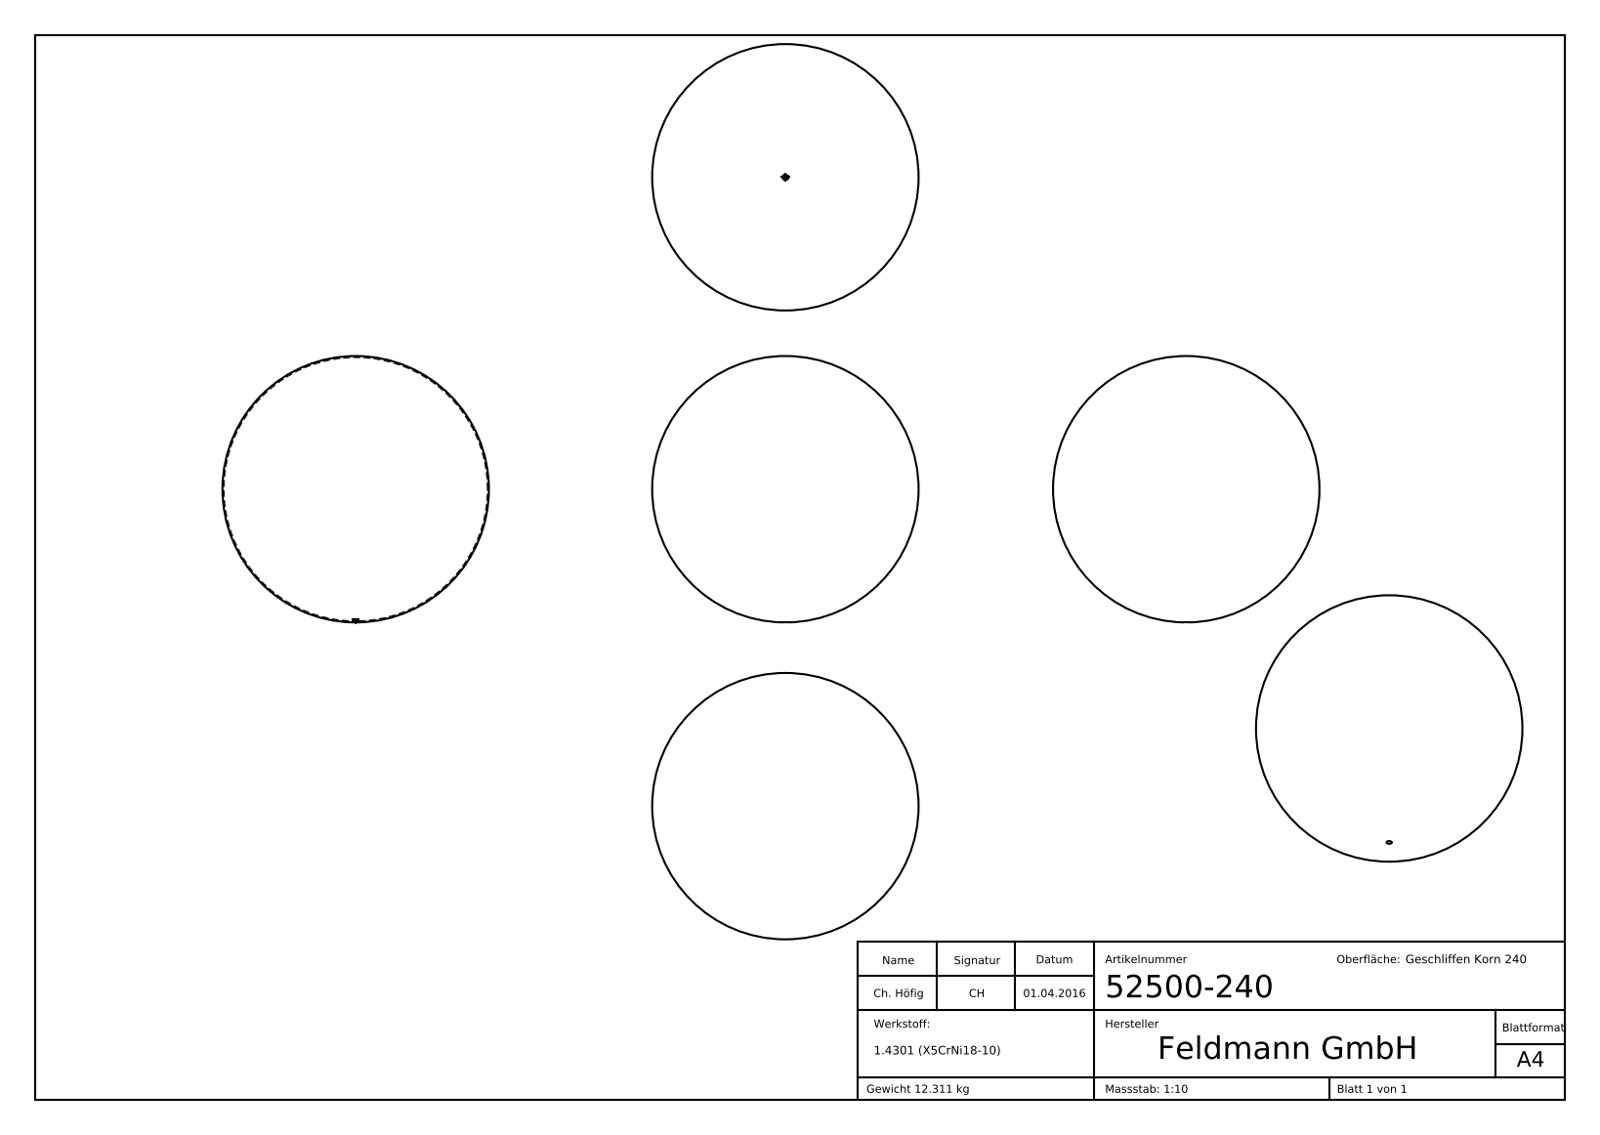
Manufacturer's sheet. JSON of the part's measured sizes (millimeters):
{"part_name": "52500-240", "step_written_by": "SolidWorks 2015 (CONFIG_CONTROL_DESIGN)", "units": "millimeters", "bodies": {"solids": 1, "faces": 233, "planar": 96, "cylindrical": 4, "other": 133}, "overall_size": [500, 500, 499.95], "volume_mm3": 1558000, "surface_area_mm2": 1558000, "round_holes": [[8.5, 1]], "round_bosses_or_shafts": [[12, 1]]}
